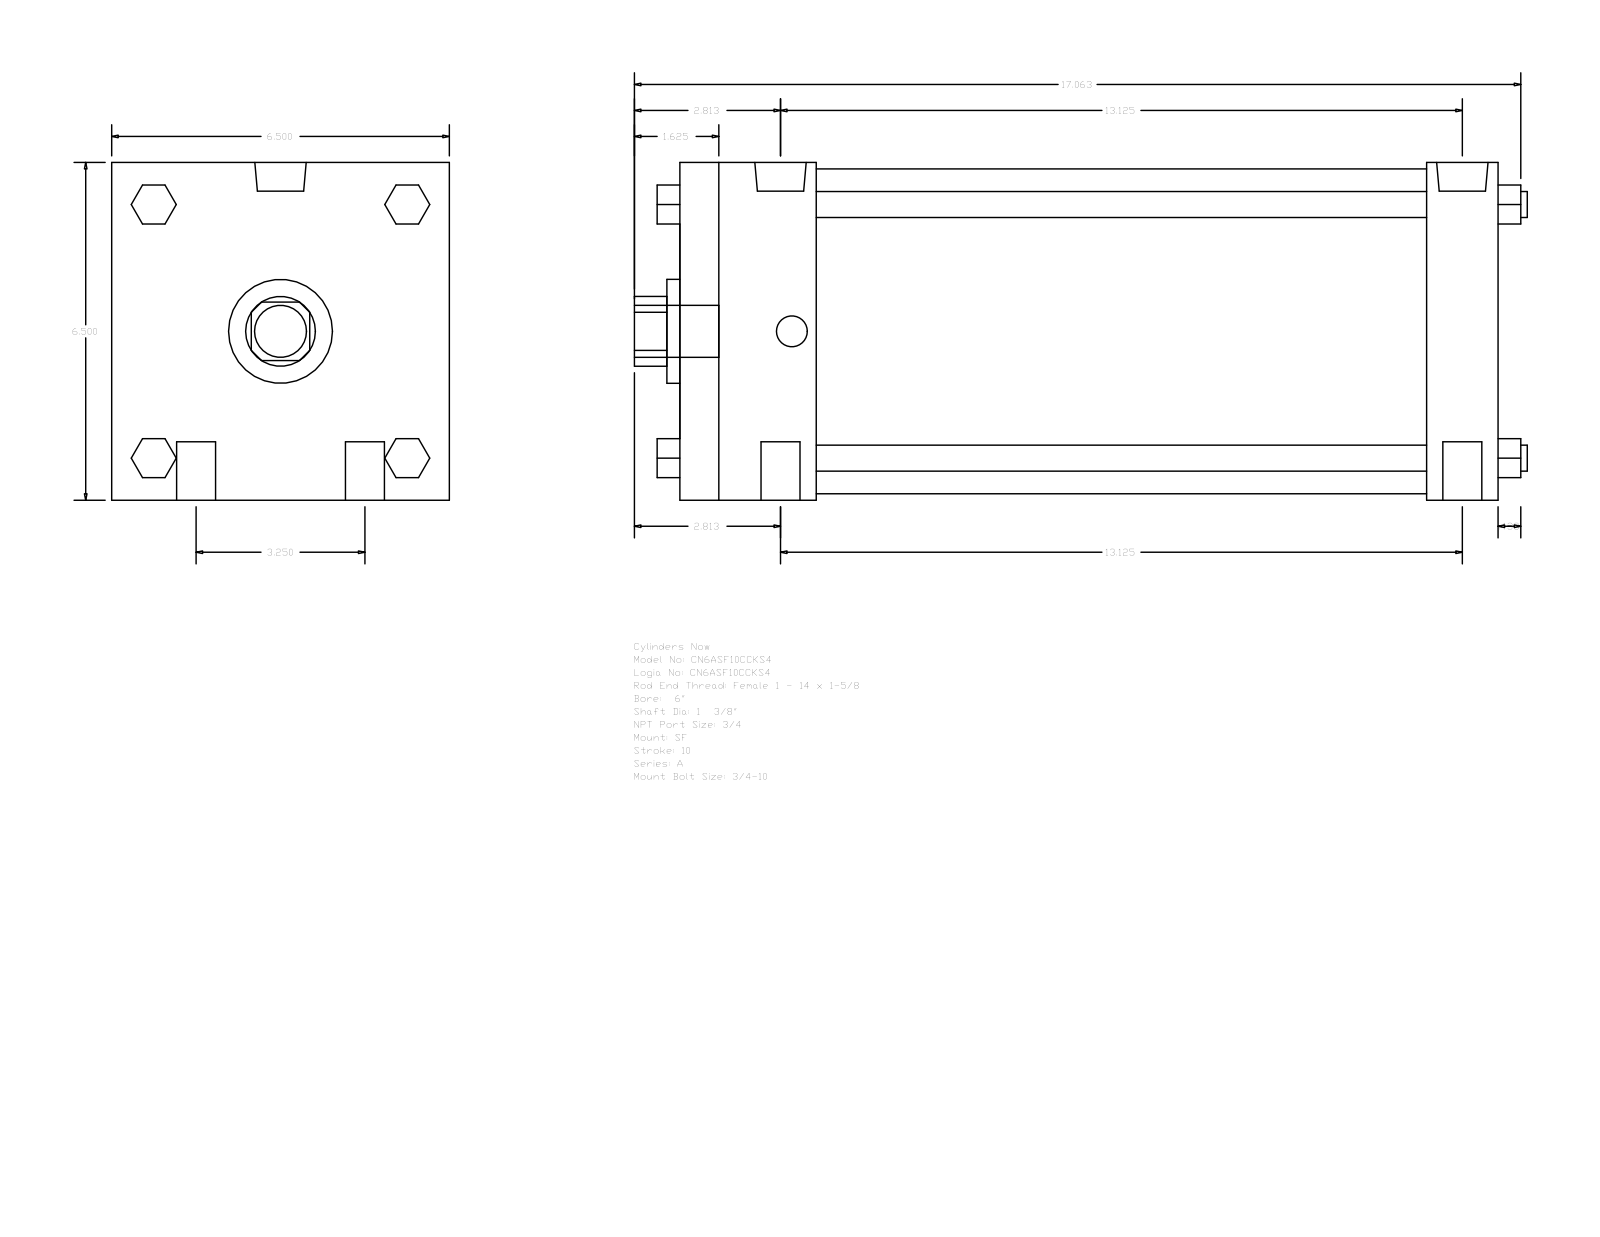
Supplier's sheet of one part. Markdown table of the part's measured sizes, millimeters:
| quantity | value |
| --- | --- |
| part name | A_SF__0600_1.375 |
| STEP written by | GSSL Pune (CONFIG_CONTROL_DESIGN) |
| units | millimeters |
| bodies | 0 solids, 124 faces (94 planar, 30 cylindrical, 0 other) |
| overall size | 436.56 × 165.1 × 165.1 |
| round holes (diameter × count) | 34.92 × 1, 50.8 × 1, 158.75 × 1 |
| round bosses / shafts (diameter × count) | 19.05 × 4, 12.7 × 4, 25.12 × 2, 15.08 × 2, 25.4 × 1 |
| partial cylindrical surfaces (radius × count) | 17.06 × 1 |
| main face-to-face distances | 165.1, 400.04, 365.12, 34.92, 66.67, 298.45, 333.37, 19.05, 61.97, 107.34 |
